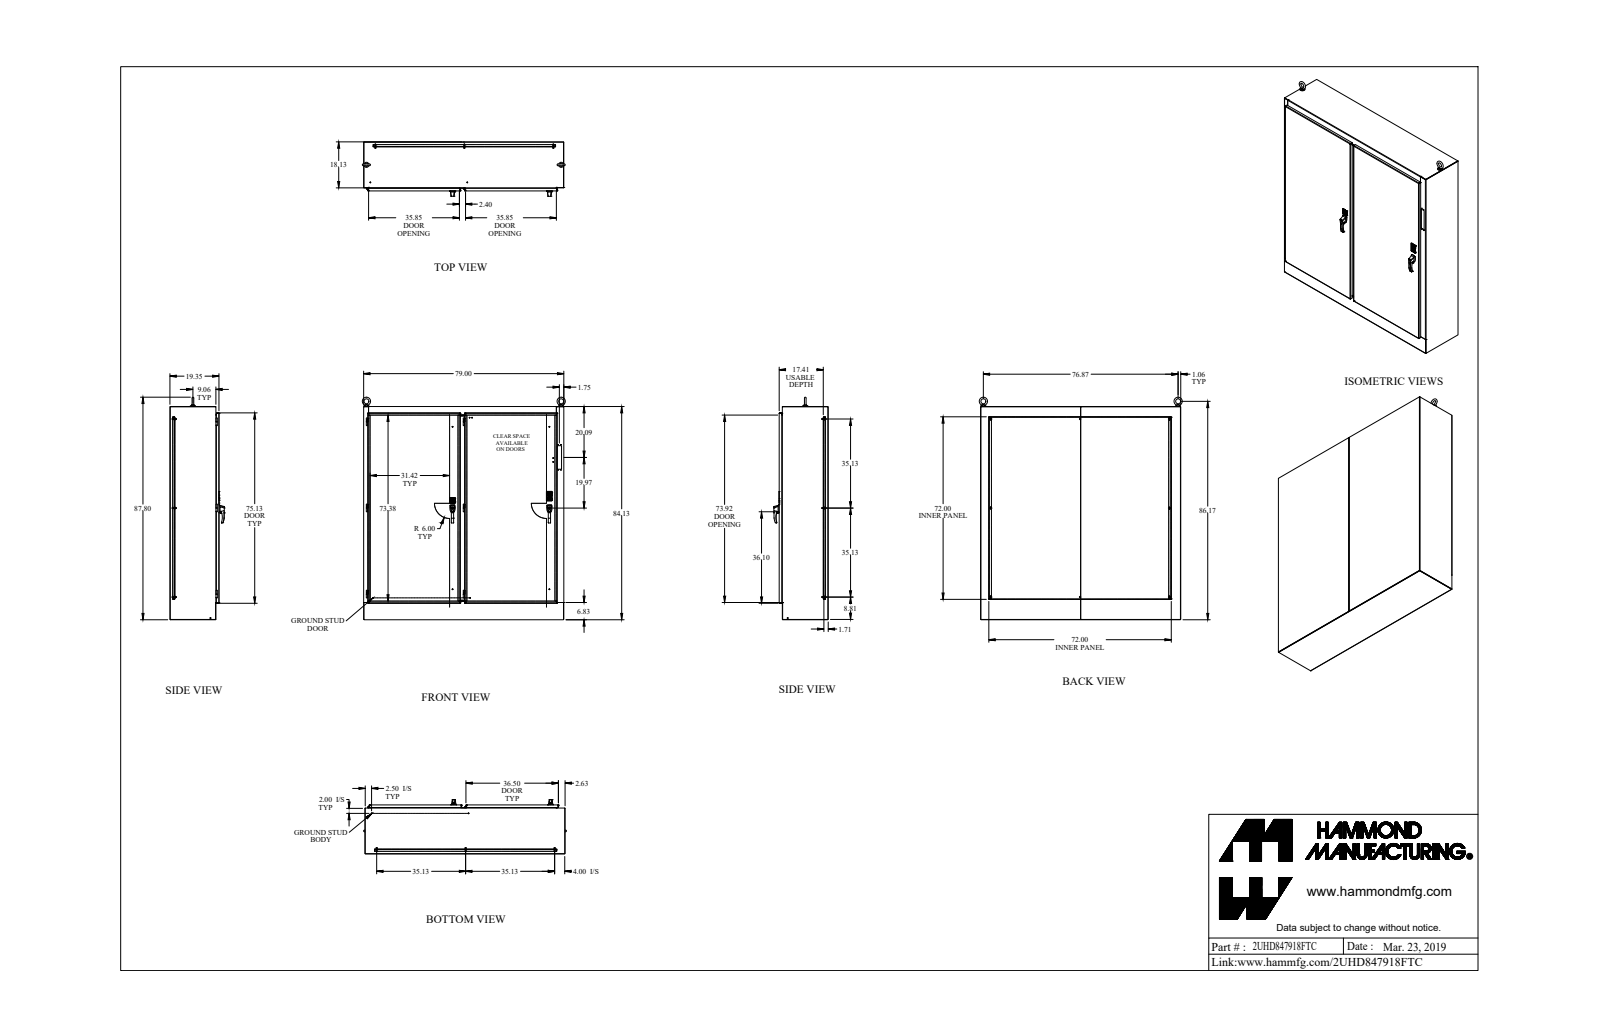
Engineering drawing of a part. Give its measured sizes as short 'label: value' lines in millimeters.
name: 2UHD847918FTC
written by: SolidWorks 2018 (AUTOMOTIVE_DESIGN)
unit: mm
bodies: 217 solids, 3088 faces (1806 planar, 908 cylindrical, 374 other)
size: 2230.1 × 2035.1 × 545.2
volume: 87 460 000 mm³; area: 37 360 000 mm²
holes: 12× ⌀5, 11× ⌀7.1, 11× ⌀7.8, 10× ⌀6.4, 8× ⌀8.9, 6× ⌀6.5, 6× ⌀8, 5× ⌀11.3, 4× ⌀7.1, 4× ⌀7.2, 4× ⌀9.5, 4× ⌀9.9
bosses: 19× ⌀6.4, 12× ⌀25.4, 9× ⌀16.5, 9× ⌀9.5, 9× ⌀8.4, 8× ⌀7.1, 6× ⌀19.1, 6× ⌀13.5
rounds: 62× R3.2, 55× R1.5, 42× R12.7, 34× R4.7, 28× R0.8, 16× R0.4, 16× R0.5, 12× R0.8
face distances: 3.2, 1.2, 442.7, 492, 488.8, 49.2, 46, 48, 44.8, 443.9
hole spacings: 971.5, 25.4, 50.8, 28.6, 32.7, 785.8, 814.4, 814.6
